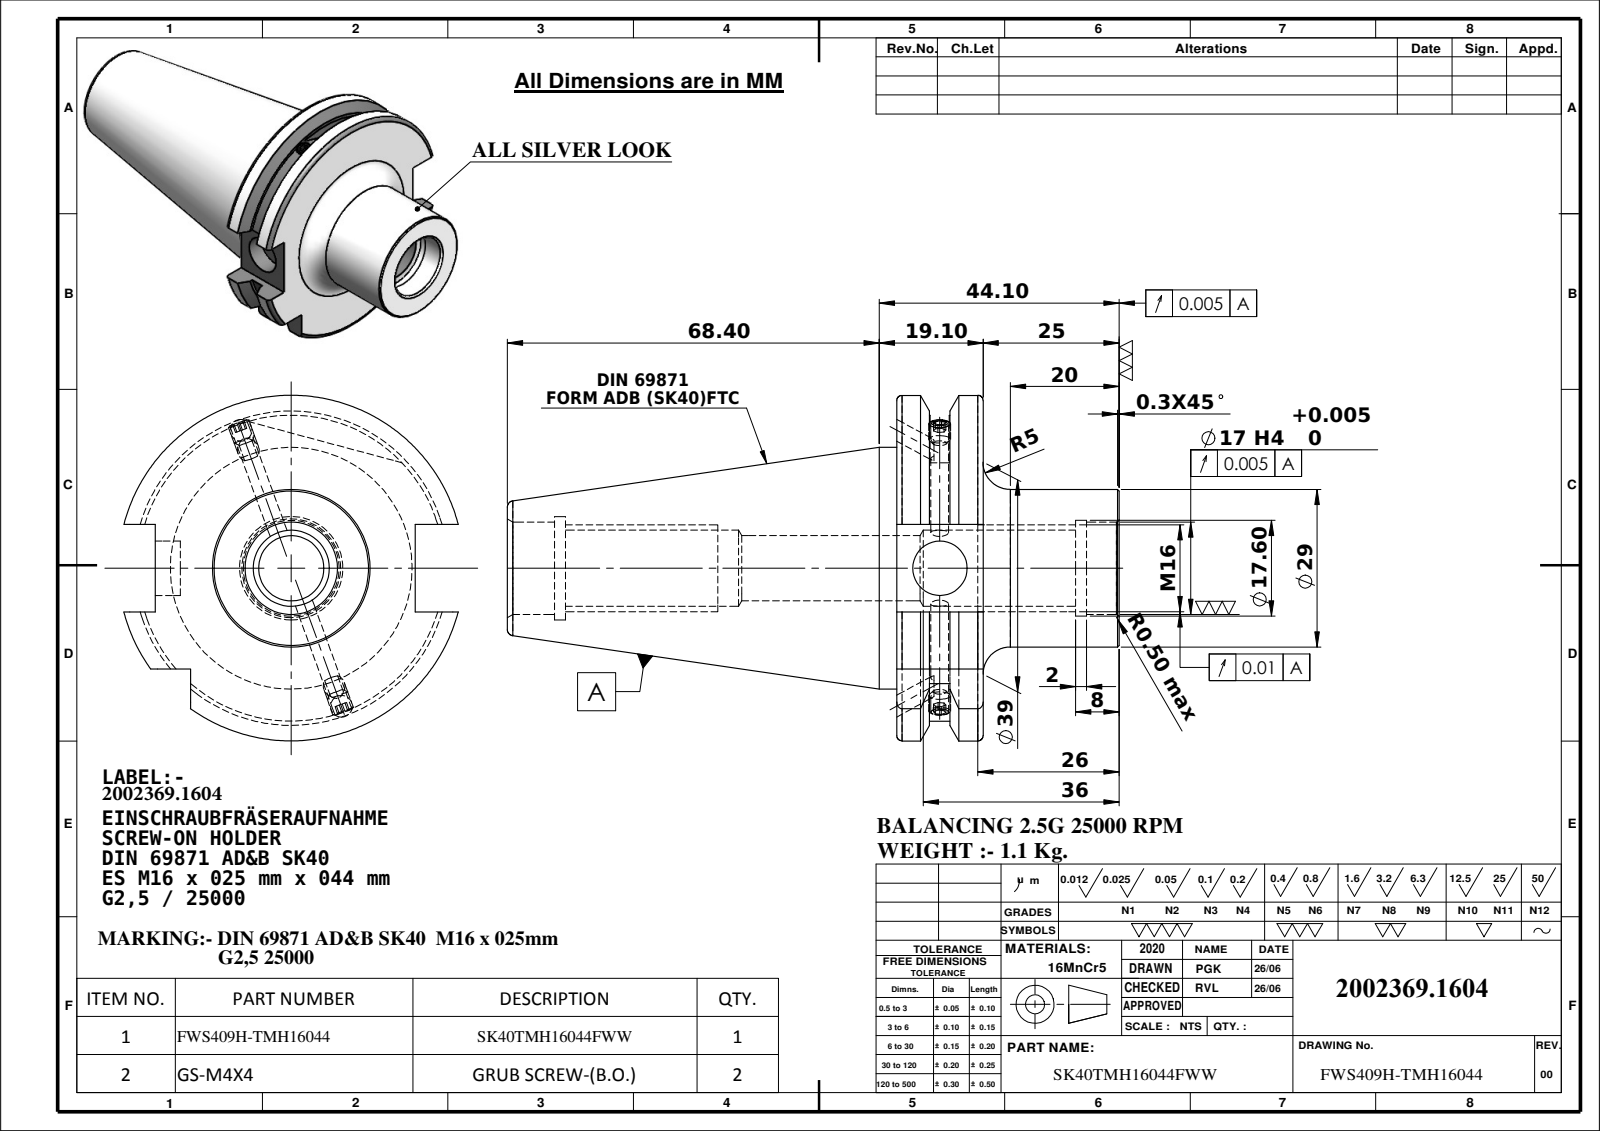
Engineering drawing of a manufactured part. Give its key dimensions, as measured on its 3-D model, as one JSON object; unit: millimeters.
{"part_name": "91406-ES7M16025; M4X4.IGS; SK40TMH16044FWW.IGS", "step_written_by": "SolidWorks 2018 (AUTOMOTIVE_DESIGN)", "units": "millimeters", "bodies": {"solids": 3, "faces": 132, "planar": 0, "cylindrical": 0, "other": 132}, "overall_size": [112.5, 63.55, 61.48], "volume_mm3": 112335, "surface_area_mm2": 24536}
